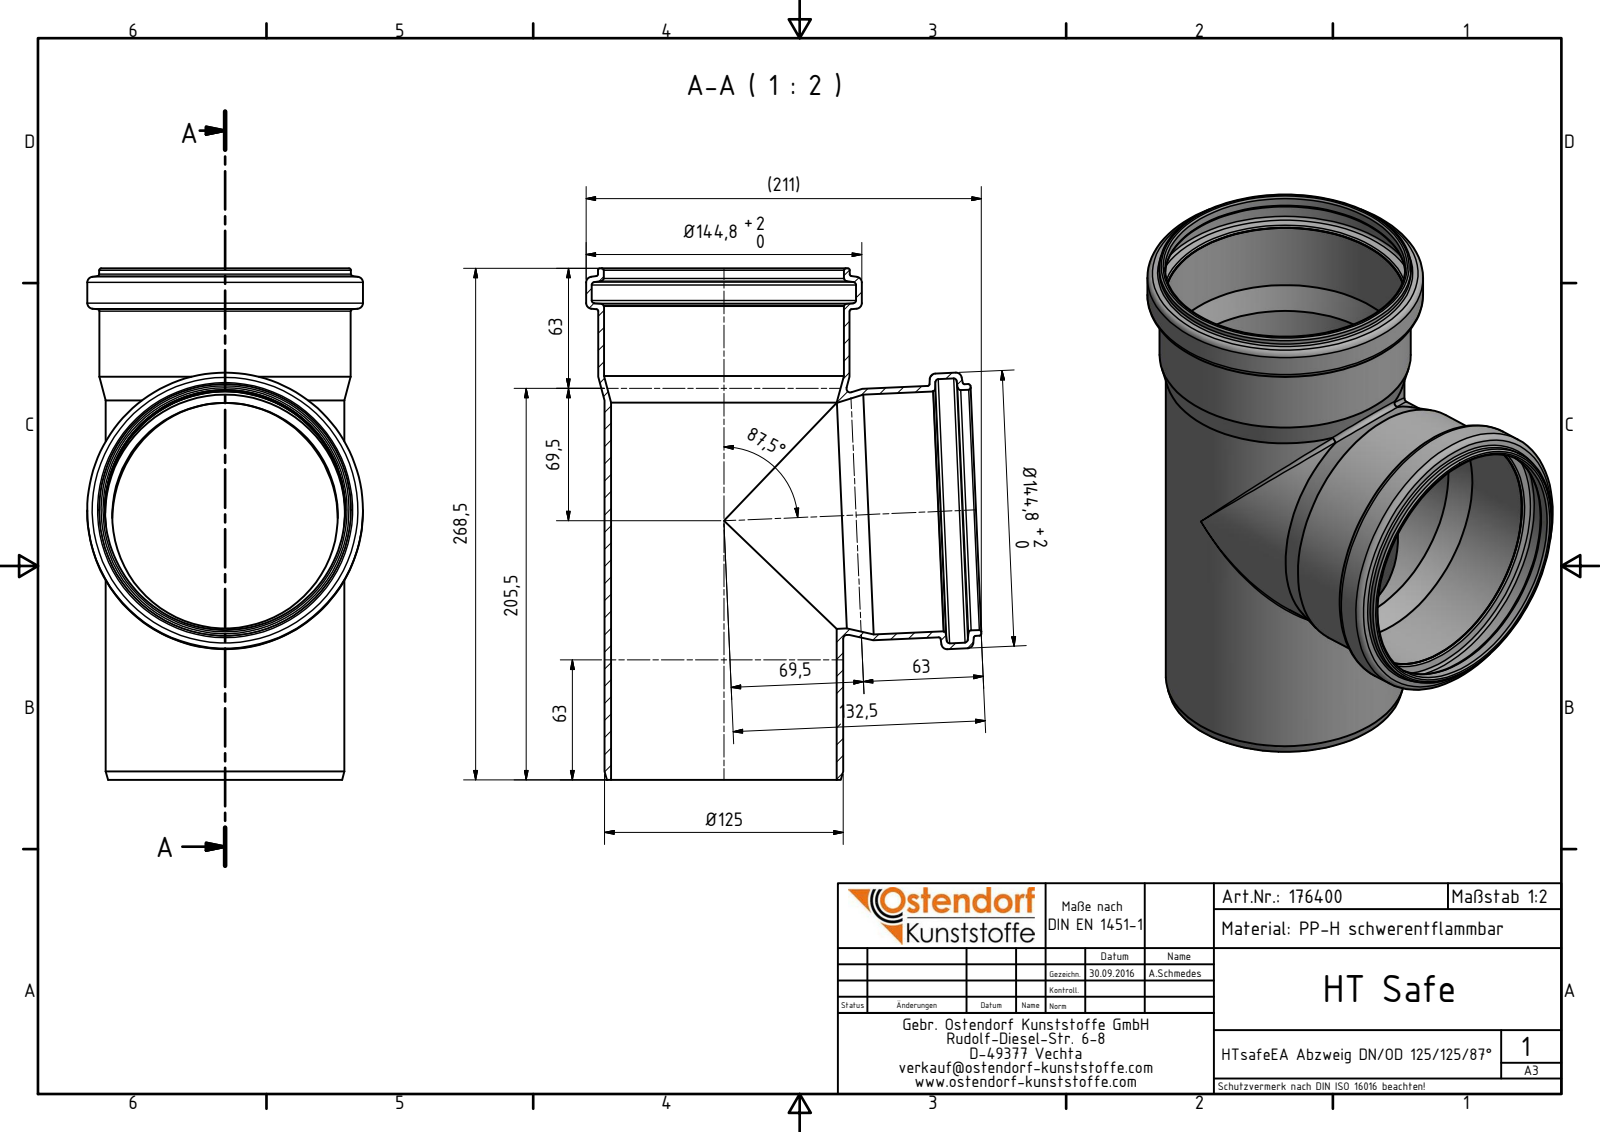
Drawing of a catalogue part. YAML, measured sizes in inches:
part_name: "176400 HTsafeEA DN_OD 125_125_87°"
step_written_by: "Autodesk Inventor 2016 (AUTOMOTIVE_DESIGN)"
units: inches
bodies: {solids: 1, faces: 60, planar: 5, cylindrical: 18, other: 37}
overall_size: [10.571, 8.174, 5.701]
volume: 26.74
surface_area: 425
round_holes:
  - {diameter: 4.665, count: 2}
  - {diameter: 4.961, count: 2}
  - {diameter: 4.969, count: 2}
  - {diameter: 5.465, count: 2}
round_bosses_or_shafts:
  - {diameter: 5.701, count: 2}
  - {diameter: 5.205, count: 2}
  - {diameter: 5.197, count: 2}
  - {diameter: 4.933, count: 2}
face_to_face_distances: [10.571, 0.779, 9.792]
